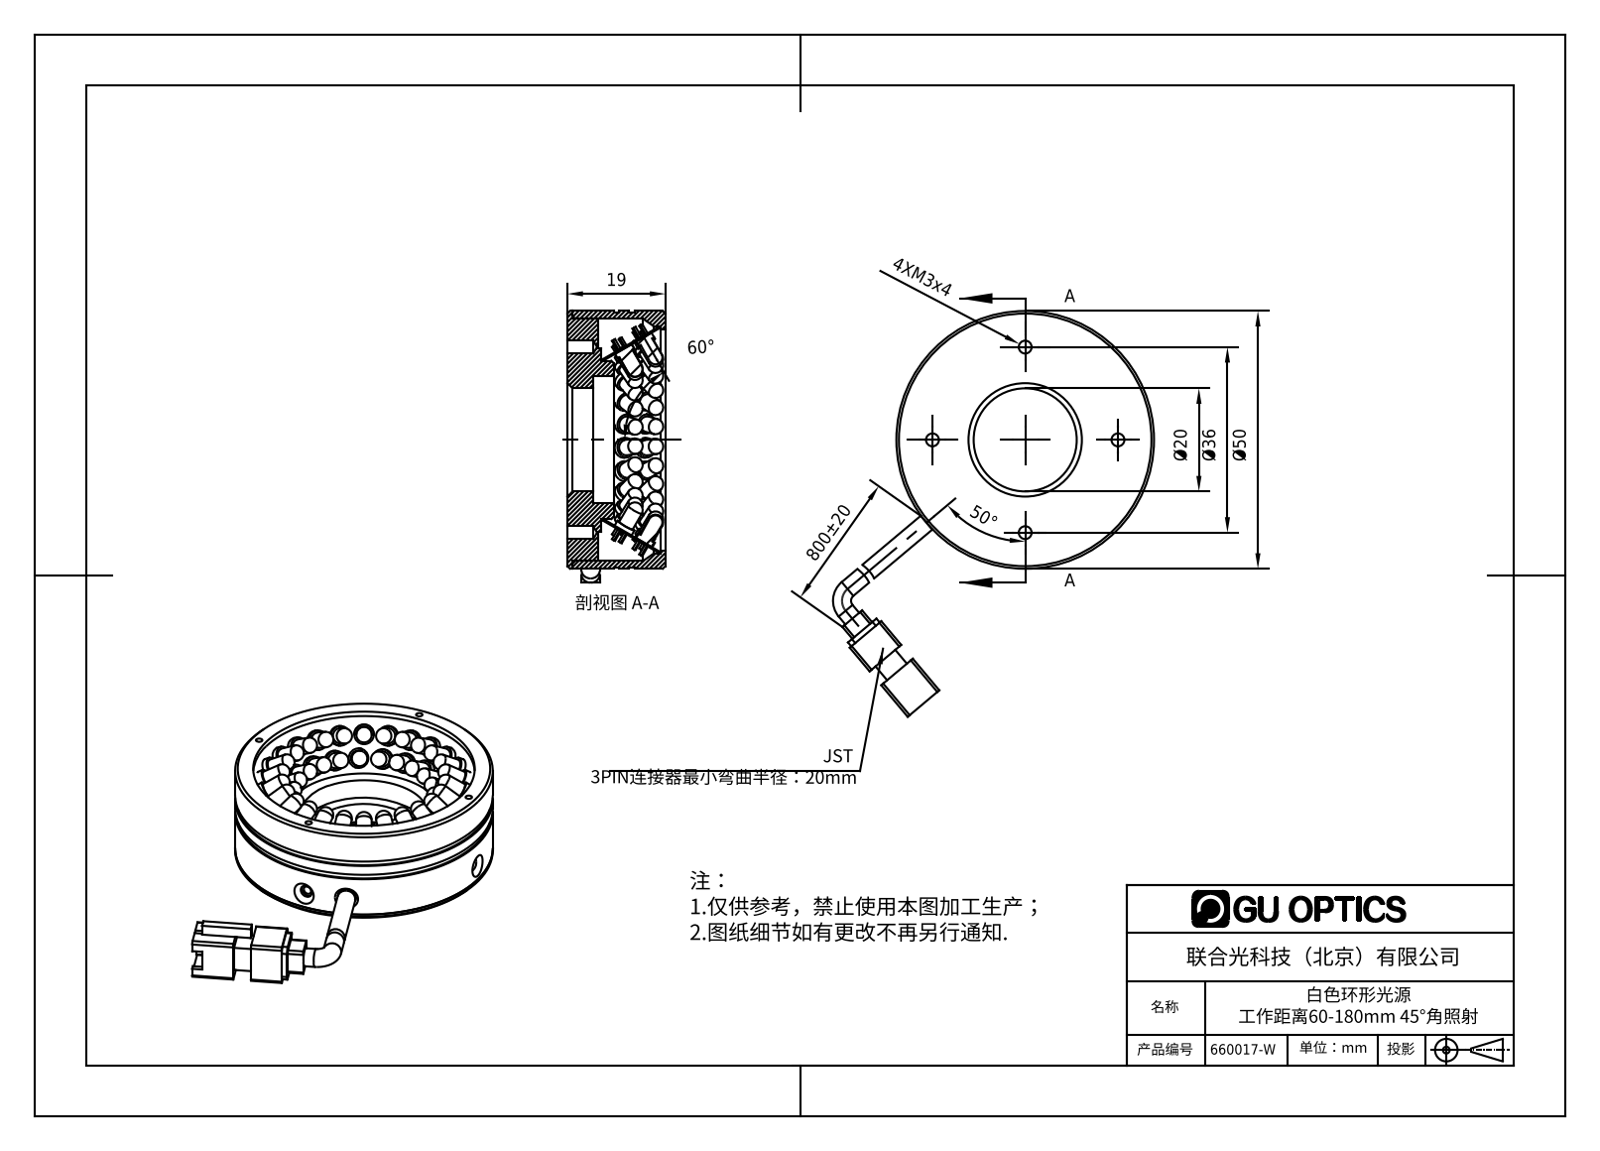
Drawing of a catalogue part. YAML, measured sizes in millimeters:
part_name: "660017-W"
step_written_by: "SolidWorks 2016 (AUTOMOTIVE_DESIGN)"
units: millimeters
bodies: {solids: 54, faces: 1066, planar: 662, cylindrical: 300, other: 104}
overall_size: [82.93, 50, 19]
volume: 17639
surface_area: 20260
round_holes:
  - {diameter: 1.25, count: 4}
  - {diameter: 2.5, count: 4}
  - {diameter: 1.6, count: 2}
  - {diameter: 2.4, count: 2}
  - {diameter: 3, count: 2}
  - {diameter: 3.6, count: 1}
  - {diameter: 20, count: 1}
  - {diameter: 24.6, count: 1}
  - {diameter: 43, count: 1}
  - {diameter: 44, count: 1}
round_bosses_or_shafts:
  - {diameter: 3.8, count: 49}
  - {diameter: 3, count: 47}
  - {diameter: 3.5, count: 2}
  - {diameter: 50, count: 1}
  - {diameter: 49.4, count: 1}
  - {diameter: 47, count: 1}
  - {diameter: 35.54, count: 1}
  - {diameter: 30.72, count: 1}
partial_cylinders:
  - {radius: 0.5, count: 12}
  - {radius: 1, count: 4}
  - {radius: 4, count: 1}
face_to_face_distances: [1, 6, 0.5, 5, 5.5, 8, 3, 13, 2.5, 1.5]
hole_center_spacings: [11.66, 20.95, 23, 32.53, 18, 25.46, 35.6, 39.63]
